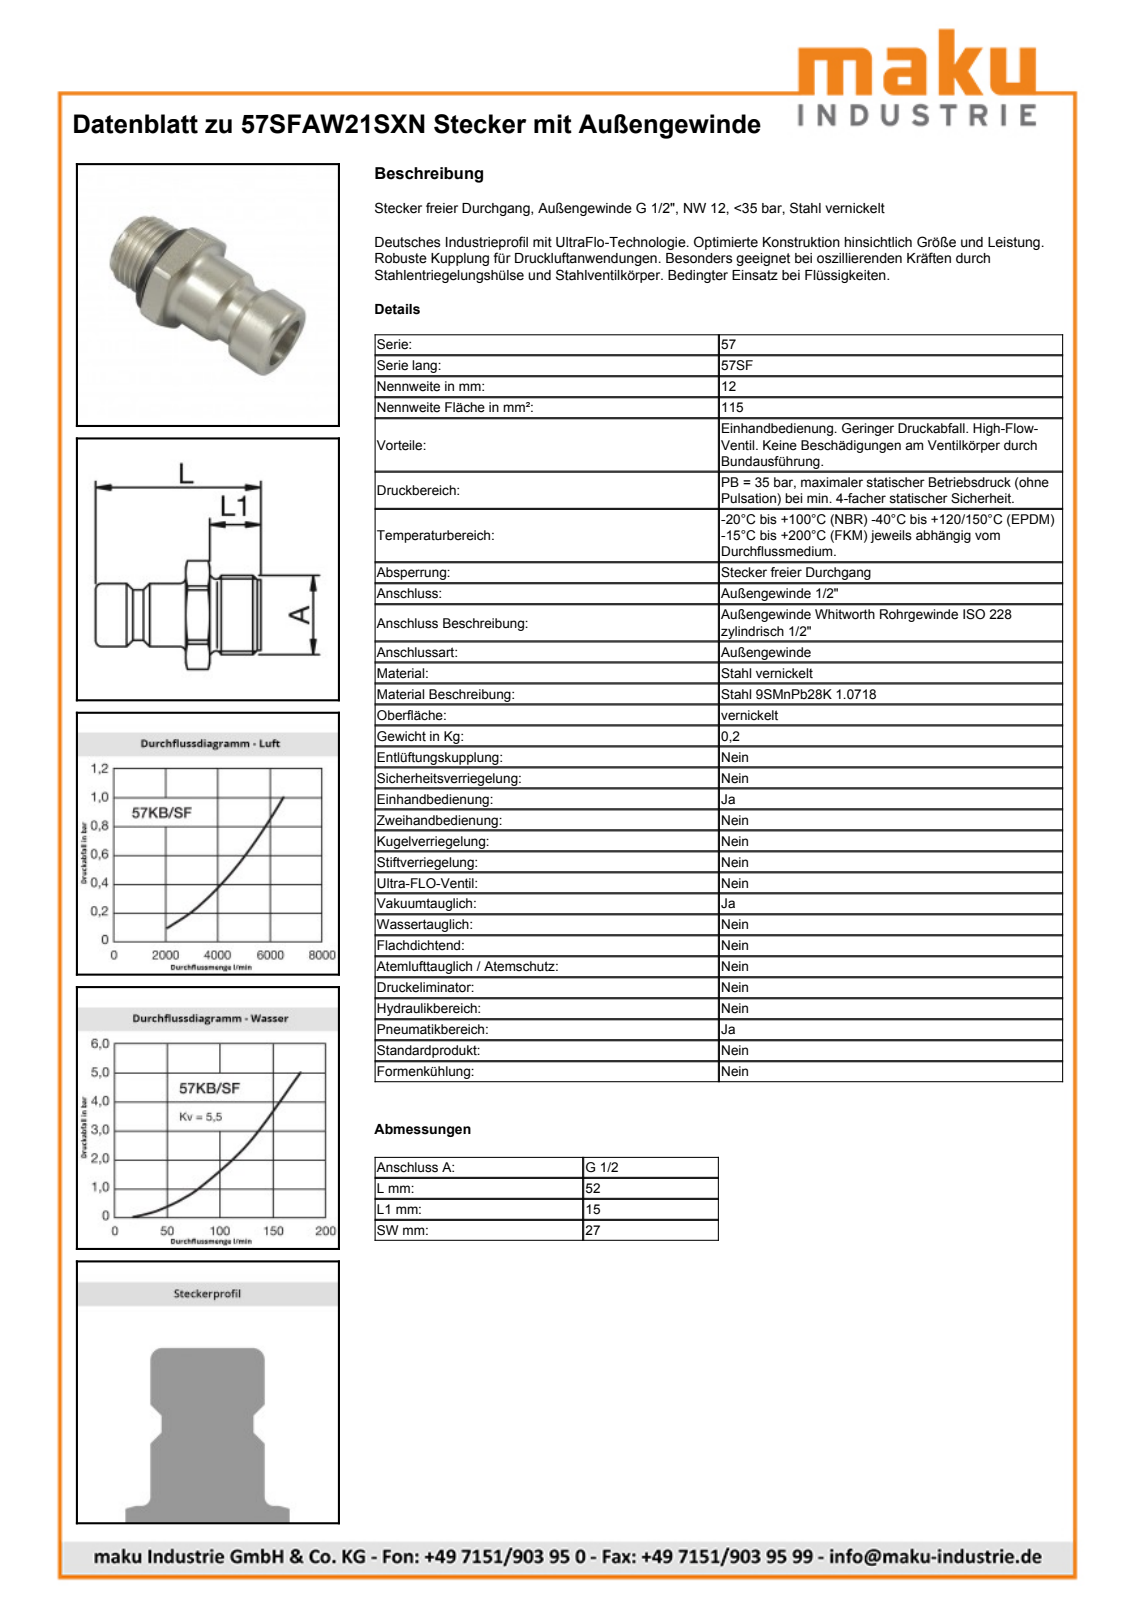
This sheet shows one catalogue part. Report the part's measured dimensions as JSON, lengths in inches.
{"part_name": "D107017; D106332; D105913", "step_written_by": "Autodesk Inventor 2013 (AUTOMOTIVE_DESIGN)", "units": "inches", "bodies": {"solids": 2, "faces": 51, "planar": 14, "cylindrical": 15, "other": 22}, "overall_size": [2.047, 1.199, 1.063], "volume_in3": 0.711, "surface_area_in2": 11.19, "round_holes": [[0.531, 1], [0.835, 1]], "round_bosses_or_shafts": [[1.004, 1], [0.825, 1], [0.823, 1], [0.709, 1], [0.661, 1]], "partial_cylinders_radius": [[0.599, 1]], "face_to_face_distances": [1.063, 0.079, 0.276, 0.354, 1.181, 1.457, 1.535, 2.047, 0.866, 0.591]}
